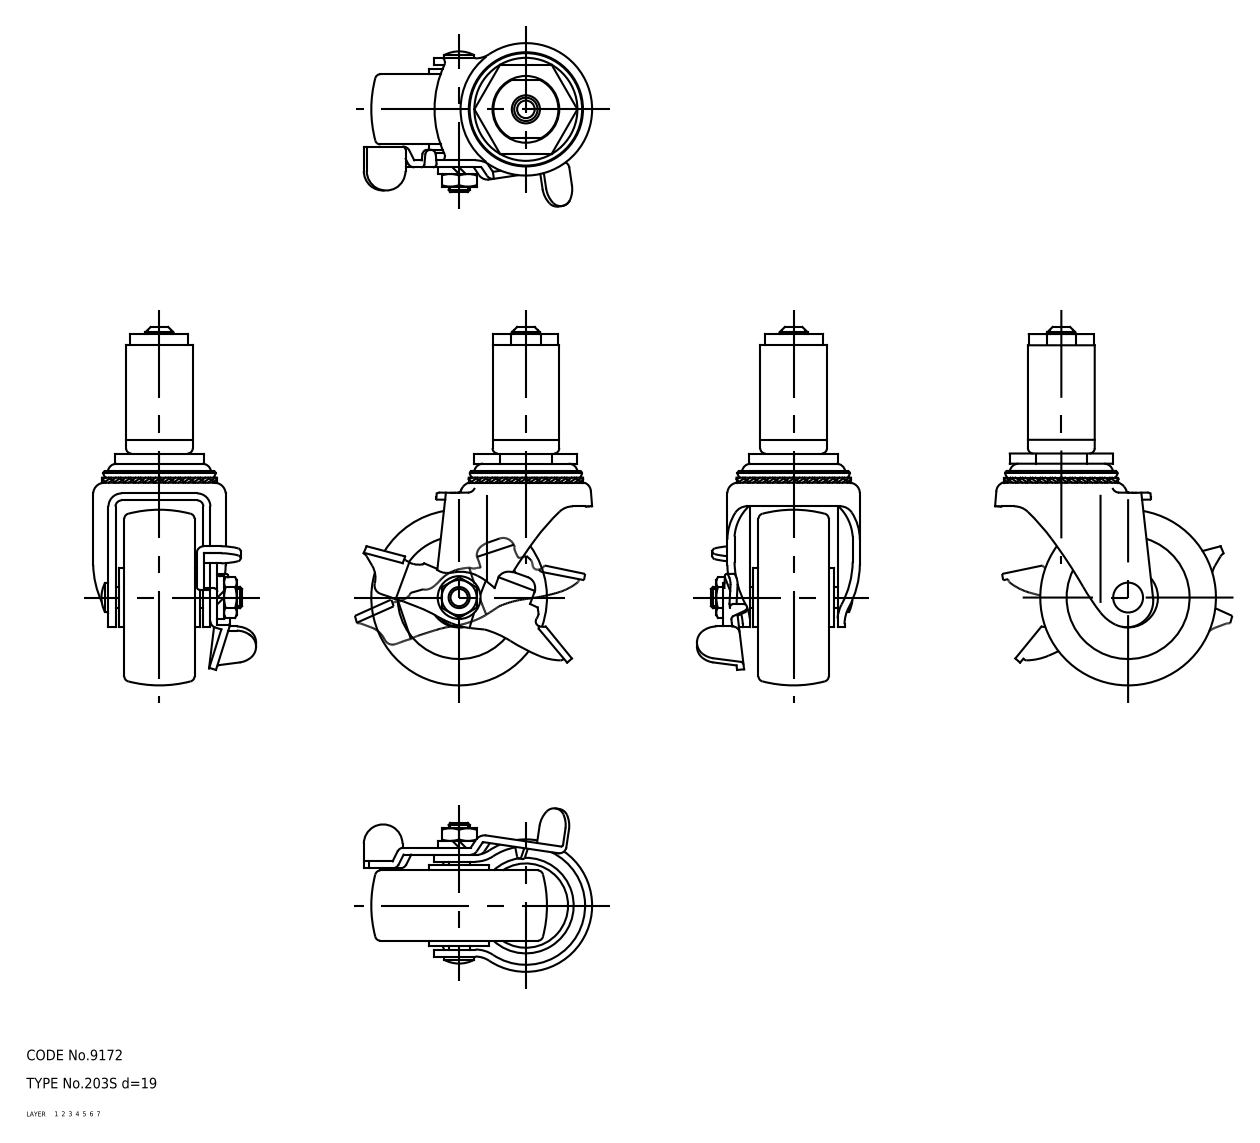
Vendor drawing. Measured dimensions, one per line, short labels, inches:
name: wheel; main shaft; lever; axle (+1 more)
written by: CADfix (AUTOMOTIVE_DESIGN)
unit: in
bodies: 5 solids, 301 faces (0 planar, 0 cylindrical, 301 other)
size: 4.016 × 2.561 × 1.826
volume: 3.804 in³; area: 35.61 in²
